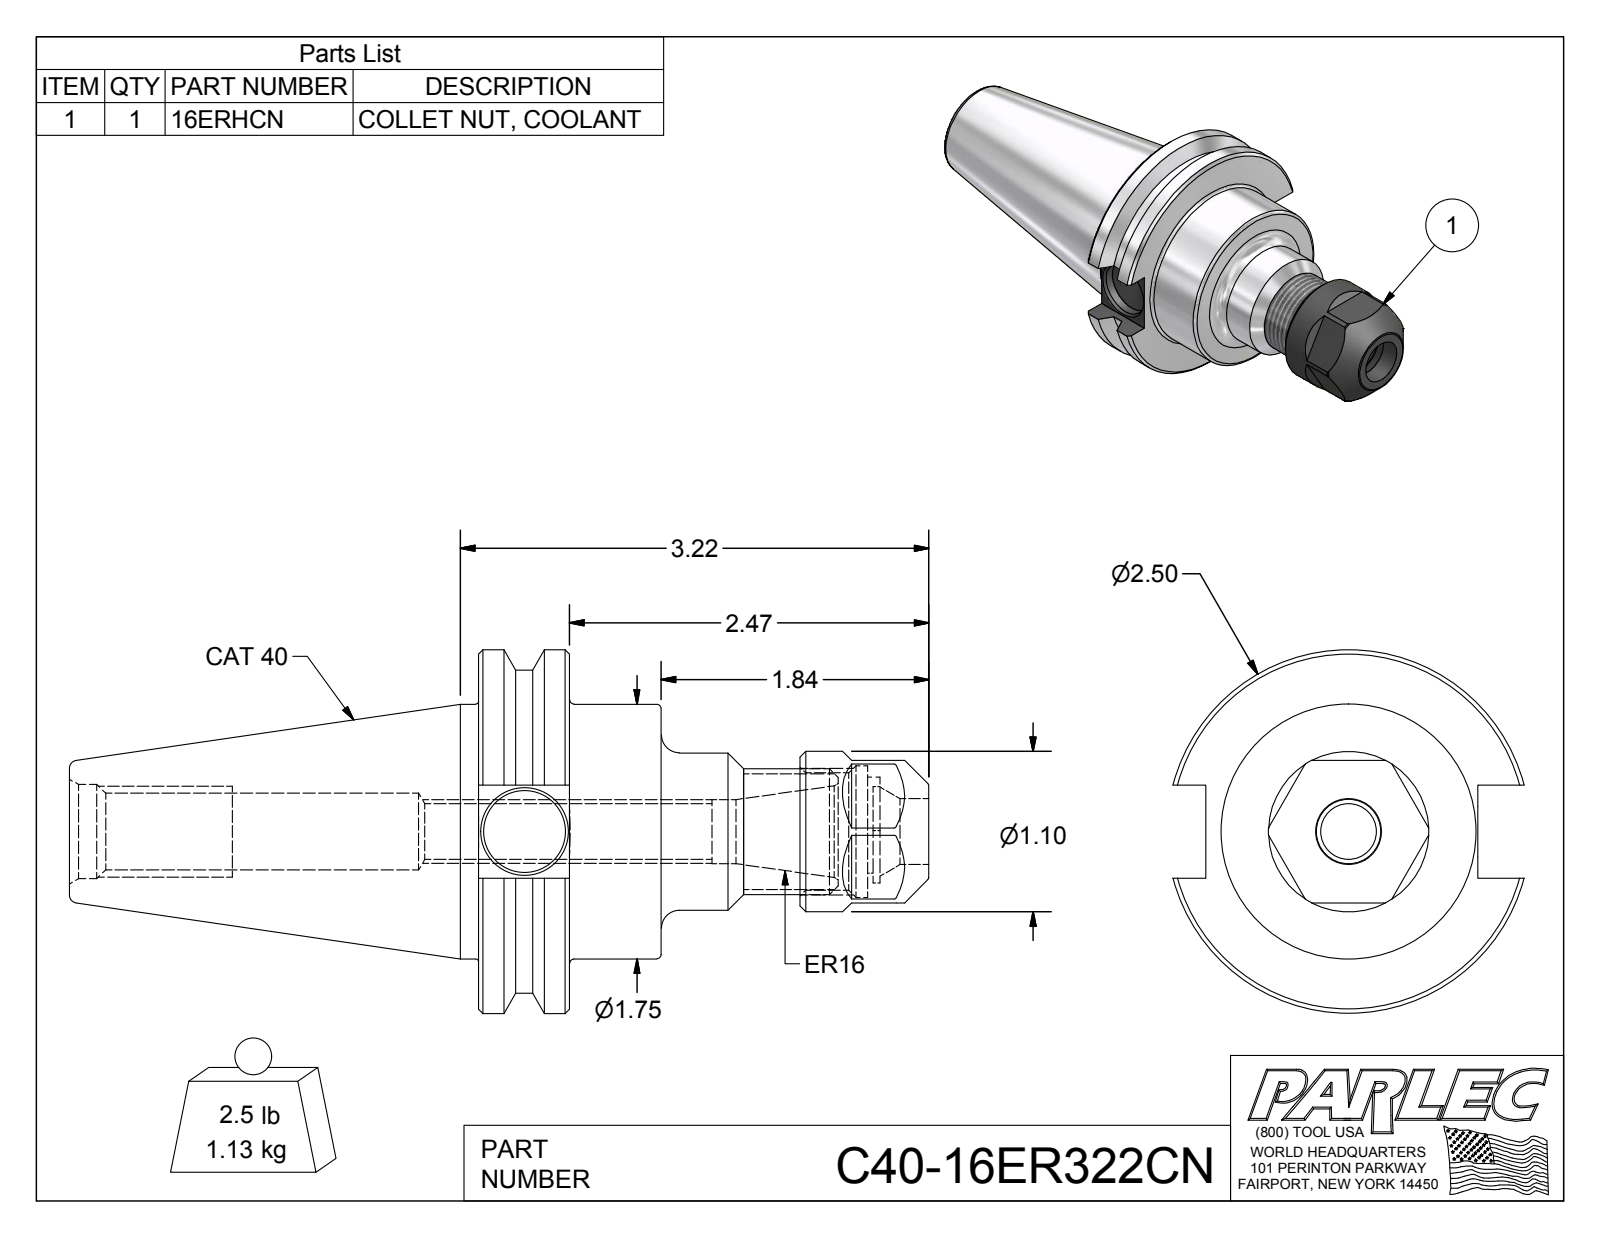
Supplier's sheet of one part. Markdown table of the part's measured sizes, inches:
| quantity | value |
| --- | --- |
| part name | C40-16ER322CN; C40-16ER3-1; 16ERHCN |
| STEP written by | Autodesk Inventor 2012 (AUTOMOTIVE_DESIGN) |
| units | inches |
| bodies | 2 solids, 85 faces (29 planar, 21 cylindrical, 35 other) |
| overall size | 5.908 × 2.5 × 2.417 |
| volume | 8.719 in³ |
| surface area | 45.74 in² |
| round holes (diameter × count) | 0.383 × 1, 0.44 × 1, 0.453 × 1, 0.527 × 1, 0.563 × 1, 0.648 × 1, 0.661 × 1, 0.807 × 1, 0.906 × 1 |
| round bosses / shafts (diameter × count) | 2.5 × 1, 2.219 × 1, 1.75 × 1, 1.102 × 1, 1.08 × 1, 0.866 × 1 |
| partial cylindrical surfaces (radius × count) | 0.354 × 1 |
| main face-to-face distances | 0.625, 1.255, 0.63, 0.979, 0.169, 0.809, 2.674, 2.049, 1.419, 0.64 |
| hole center spacings | 0.051 |
